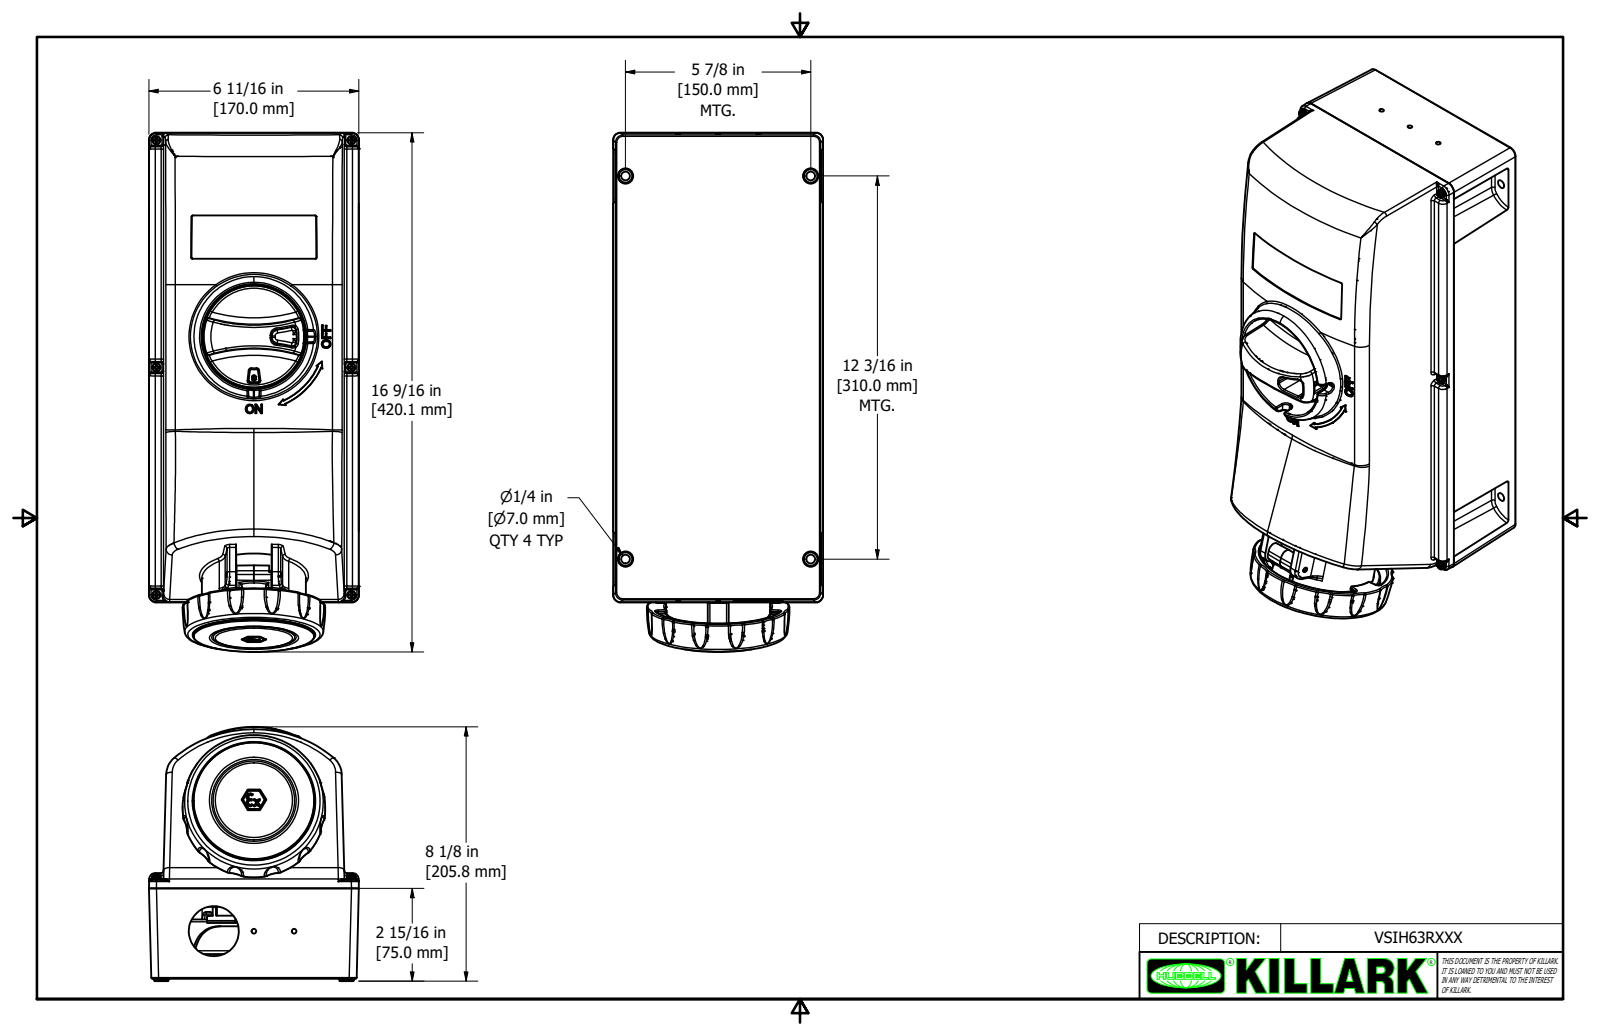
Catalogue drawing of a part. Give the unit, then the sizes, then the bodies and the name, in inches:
Units: inches
Overall size (bounding box): 16.99 × 8.1 × 6.693
Round holes (diameter × count): ⌀0.161 ×6, ⌀1.28 ×1
Round bosses / shafts (diameter × count): ⌀0.268 ×6, ⌀0.256 ×6, ⌀0.118 ×6, ⌀0.039 ×2, ⌀3.858 ×1, ⌀3.315 ×1, ⌀2.795 ×1, ⌀1.969 ×1
Partial cylindrical surfaces — rounded edges, fillets, slot ends (radius × count): R0.079 ×37, R0.039 ×10, R0.008 ×9, R0.02 ×8, R0.236 ×8, R0.059 ×4, R0.098 ×4, R0.157 ×4
Main face-to-face distances: 6.24, 14.961, 0.453, 6.693, 0.814, 0.361, 5.879, 3.366, 2.874, 0.492
Hole centre spacings: 7.244, 9.548, 6.22, 14.488, 15.767
Volume: 624.7 in³ · Surface area: 591.8 in²
Bodies: 1 solid, 874 faces (173 planar, 196 cylindrical, 505 other)
Part name (STEP PRODUCT): VSIH63RXXX (for customer)
STEP written by: Autodesk Inventor 2020 (AUTOMOTIVE_DESIGN)
